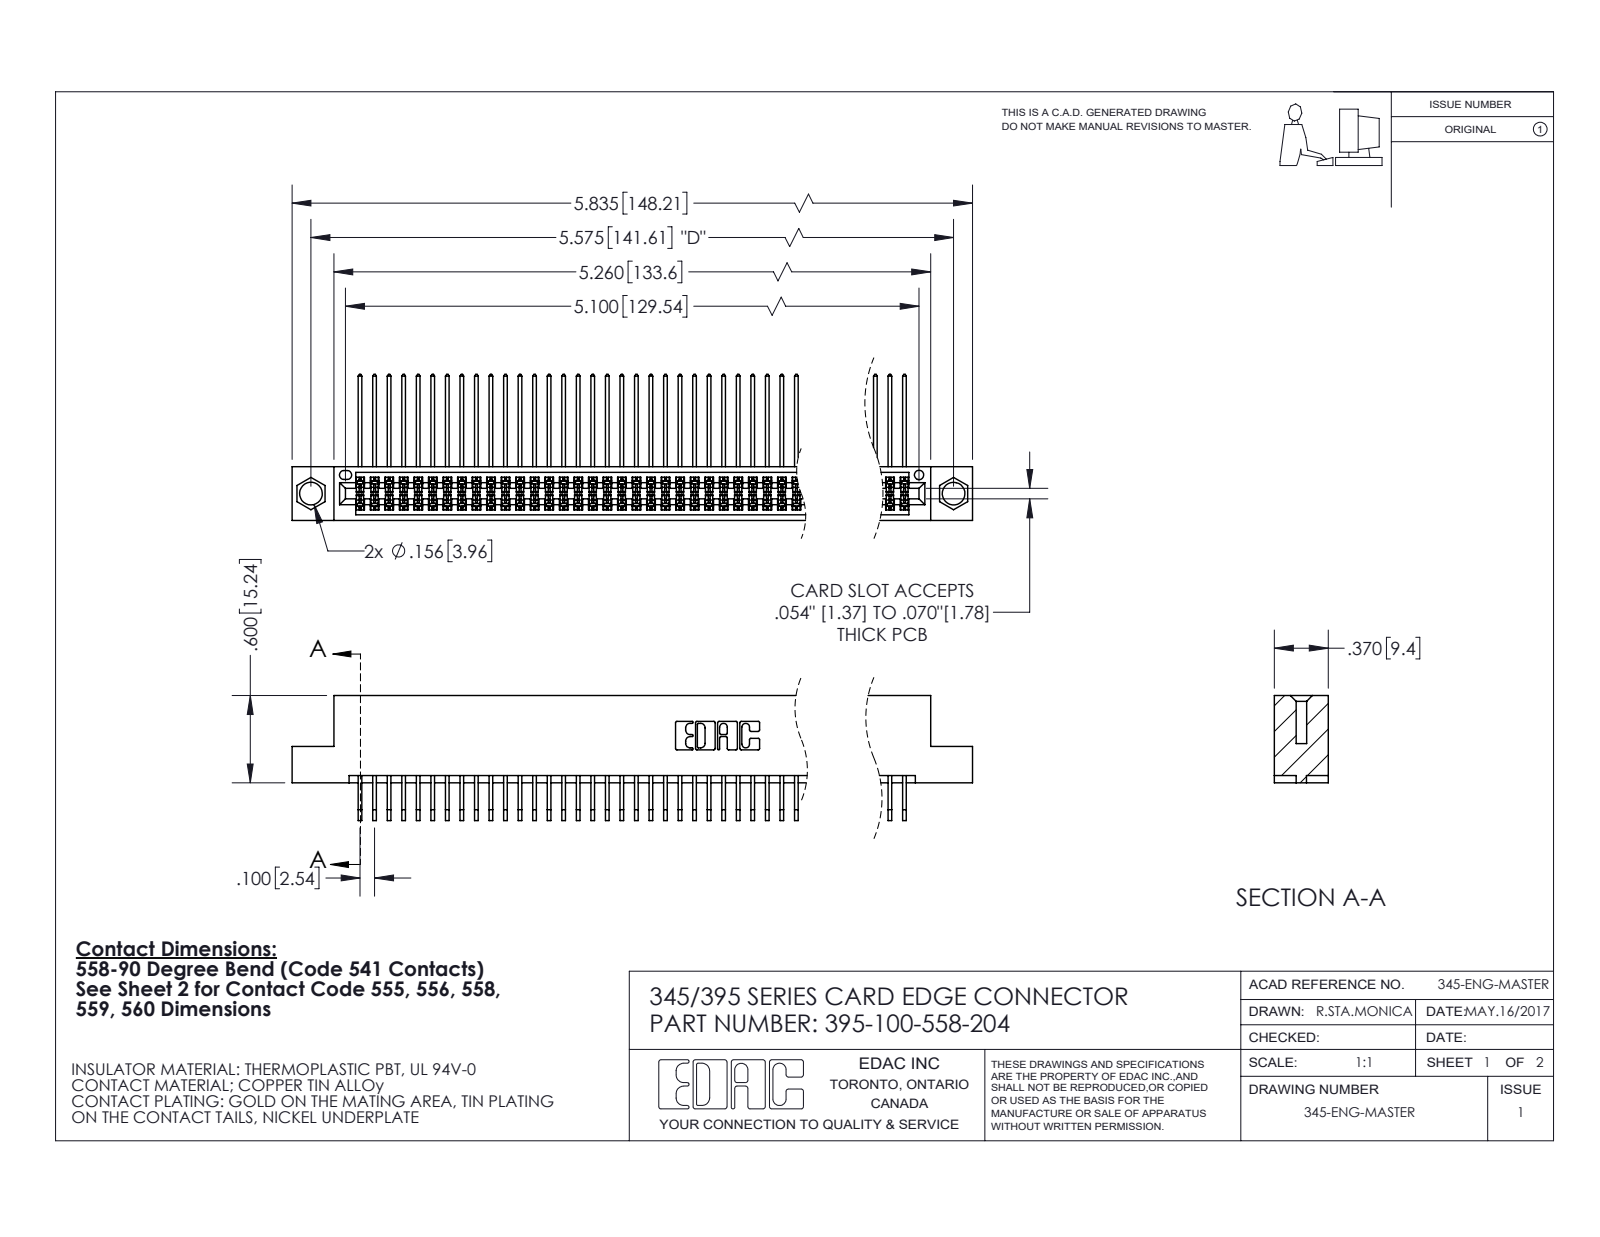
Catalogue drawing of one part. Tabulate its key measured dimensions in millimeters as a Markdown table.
| quantity | value |
| --- | --- |
| part name | 345-292-001_558 Tail - 2; 345 Part_Flush Mounting Lugs - 0.156 Dia-TI; 395-100-558-204; 345-292-001_558 559 Tail - 1 |
| STEP written by | SolidWorks 2020 (CONFIG_CONTROL_DESIGN) |
| units | millimeters |
| bodies | 101 solids, 5340 faces (3594 planar, 1746 cylindrical, 0 other) |
| overall size | 148.2 × 25.5 × 21.8 |
| volume | 14 900 mm³ |
| surface area | 24 810 mm² |
| round holes (diameter × count) | 4 × 2, 1.6 × 1 |
| partial cylindrical surfaces (radius × count) | 0.2 × 150, 0.3 × 22, 0.2 × 6, 0.8 × 6, 0.7 × 3, 0.4 × 2, 0.5 × 2, 0.6 × 2 |
| main face-to-face distances | 1.8, 7.6, 5.1, 9.4, 2.5, 6.9, 0.6, 5.7, 0.6, 4.4 |
| hole center spacings | 6.9, 135.6, 141.6 |
